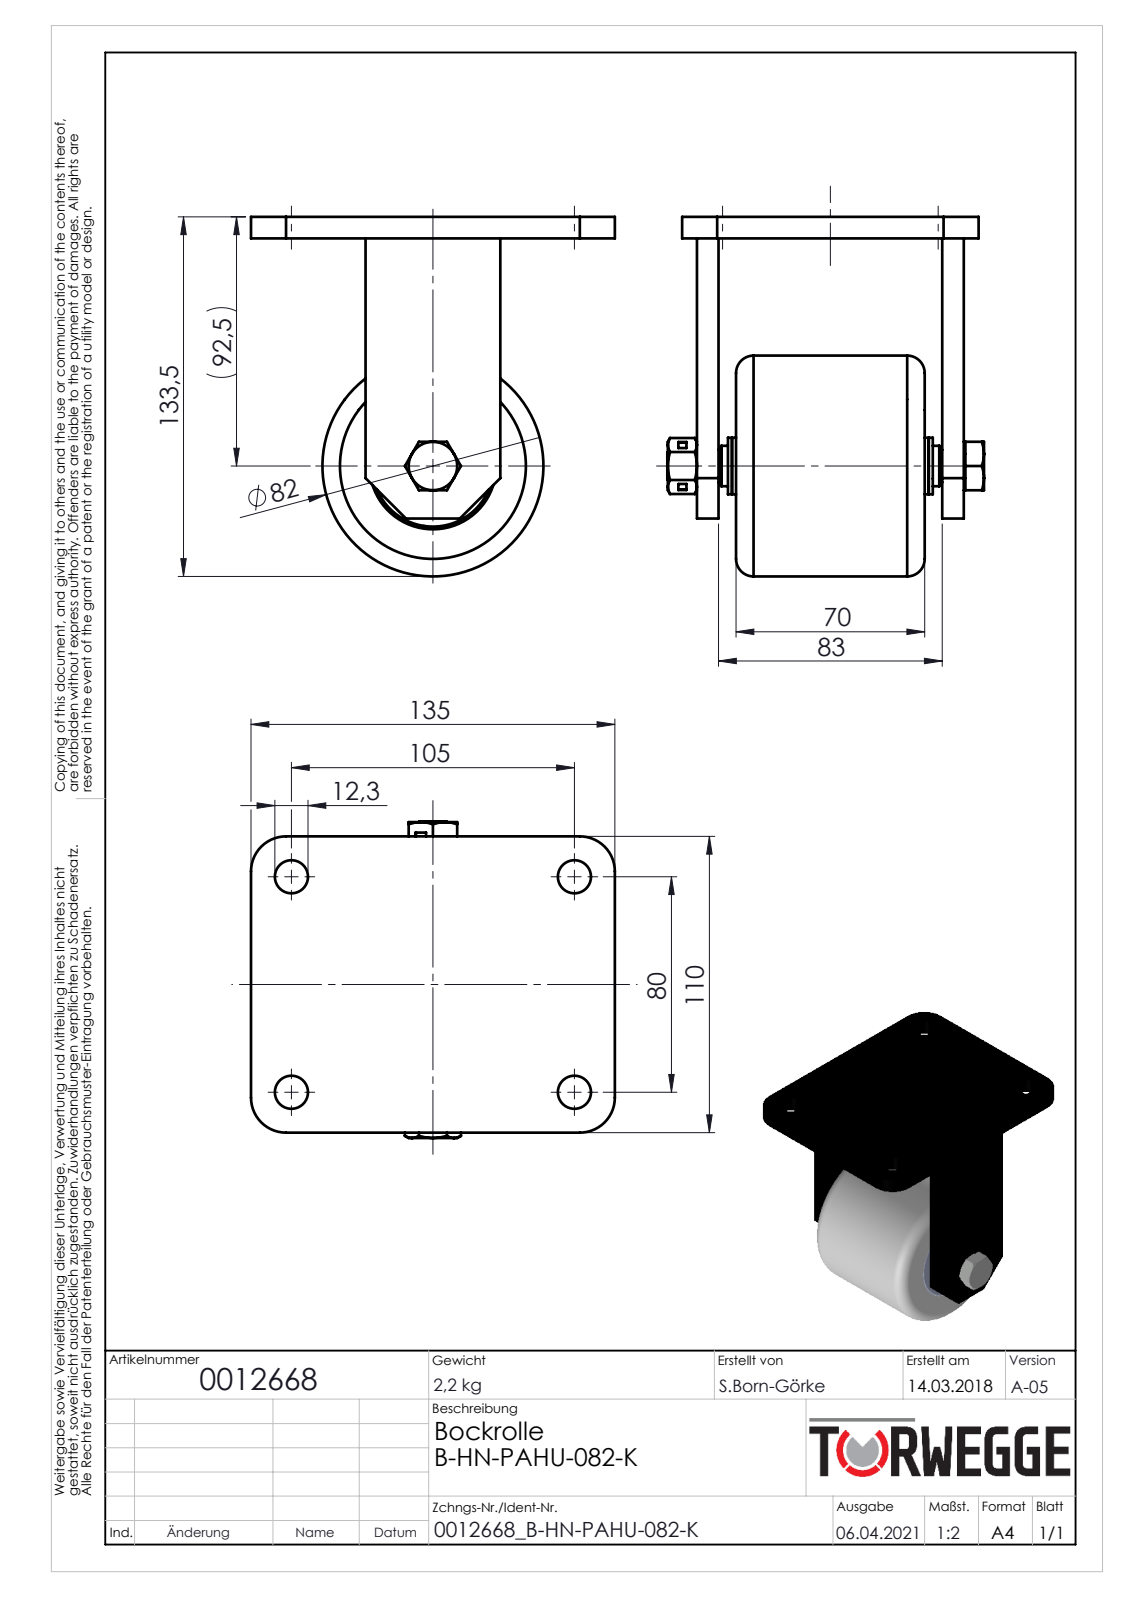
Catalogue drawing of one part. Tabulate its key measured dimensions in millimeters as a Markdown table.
| quantity | value |
| --- | --- |
| part name | 0012668 |
| STEP written by | SolidWorks 2020 (AUTOMOTIVE_DESIGN) |
| units | millimeters |
| bodies | 0 solids, 192 faces (78 planar, 64 cylindrical, 50 other) |
| overall size | 135 × 133.5 × 117.5 |
| round holes (diameter × count) | 12.3 × 4, 10.2 × 1, 12 × 1, 12.4 × 1, 15 × 1, 20 × 1, 38.9 × 1, 40 × 1, 47 × 1 |
| round bosses / shafts (diameter × count) | 82 × 1, 28.1 × 1, 21 × 1, 18 × 1 |
| partial cylindrical surfaces (radius × count) | 13 × 4 |
| main face-to-face distances | 8, 91, 76.5, 14.5, 84.5, 6.5, 99, 83, 70, 5.5 |
| hole center spacings | 80, 105, 132 |
